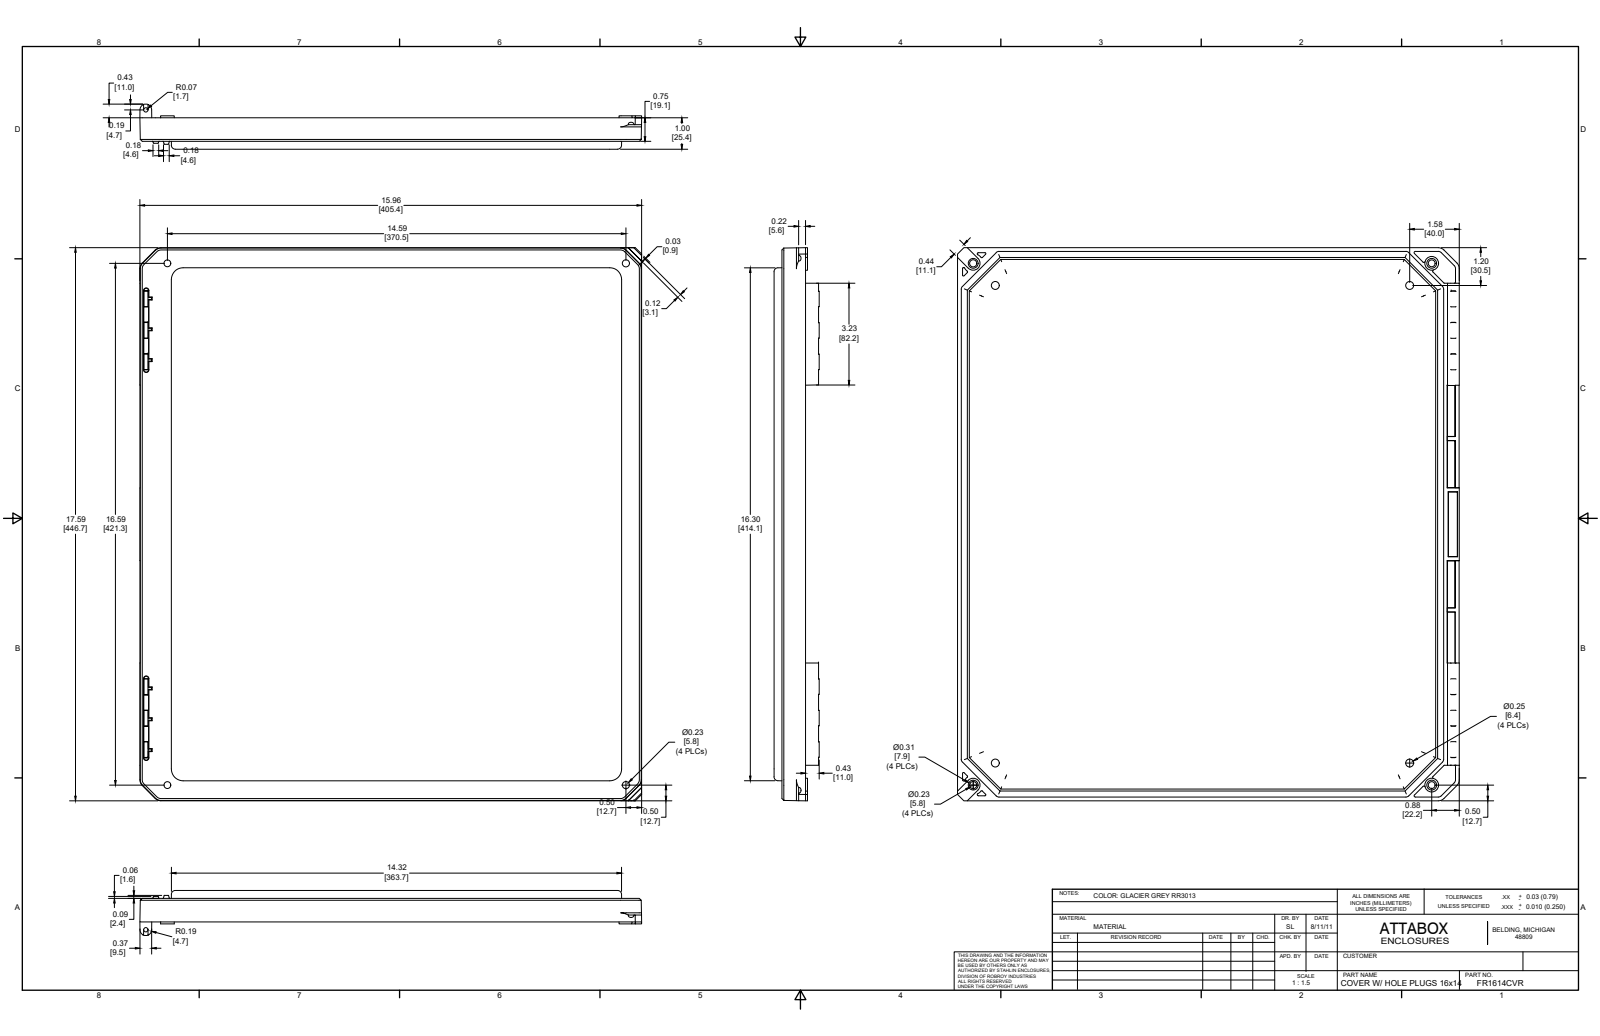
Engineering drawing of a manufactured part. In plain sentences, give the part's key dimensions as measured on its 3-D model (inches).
The part is named "FR1614CVR". Its 3-D file was written by "SolidWorks 2019 (AUTOMOTIVE_DESIGN)". It is 1 solid with 621 faces: 261 planar, 200 cylindrical and 160 other. Overall it measures 17.585 by 15.96 by 1.434 inches. Its volume is 53.86 cubic inches and its surface area 715.2 square inches. Round holes: 4 of diameter 0.253, 2 of diameter 0.219, 2 of diameter 0.227, 2 of diameter 0.313, 1 of diameter 0.137. Round bosses or shafts: 2 of diameter 0.435. Partial cylindrical surfaces (rounded edges, fillets, slot ends): 27 of radius 0.03, 18 of radius 0.01, 16 of radius 0.096, 14 of radius 0.063, 12 of radius 0.125, 10 of radius 0.04, 10 of radius 0.062, 9 of radius 0.06. The main face-to-face distances are 0.125, 0.25, 0.125, 0.375, 0.75, 0.625, 1, 0.875, 0.375, 0.625. The hole center spacings are 15.899, 0.992, 0.993, 13.182, 13.901, 13.902, 14.585, 15.182.
